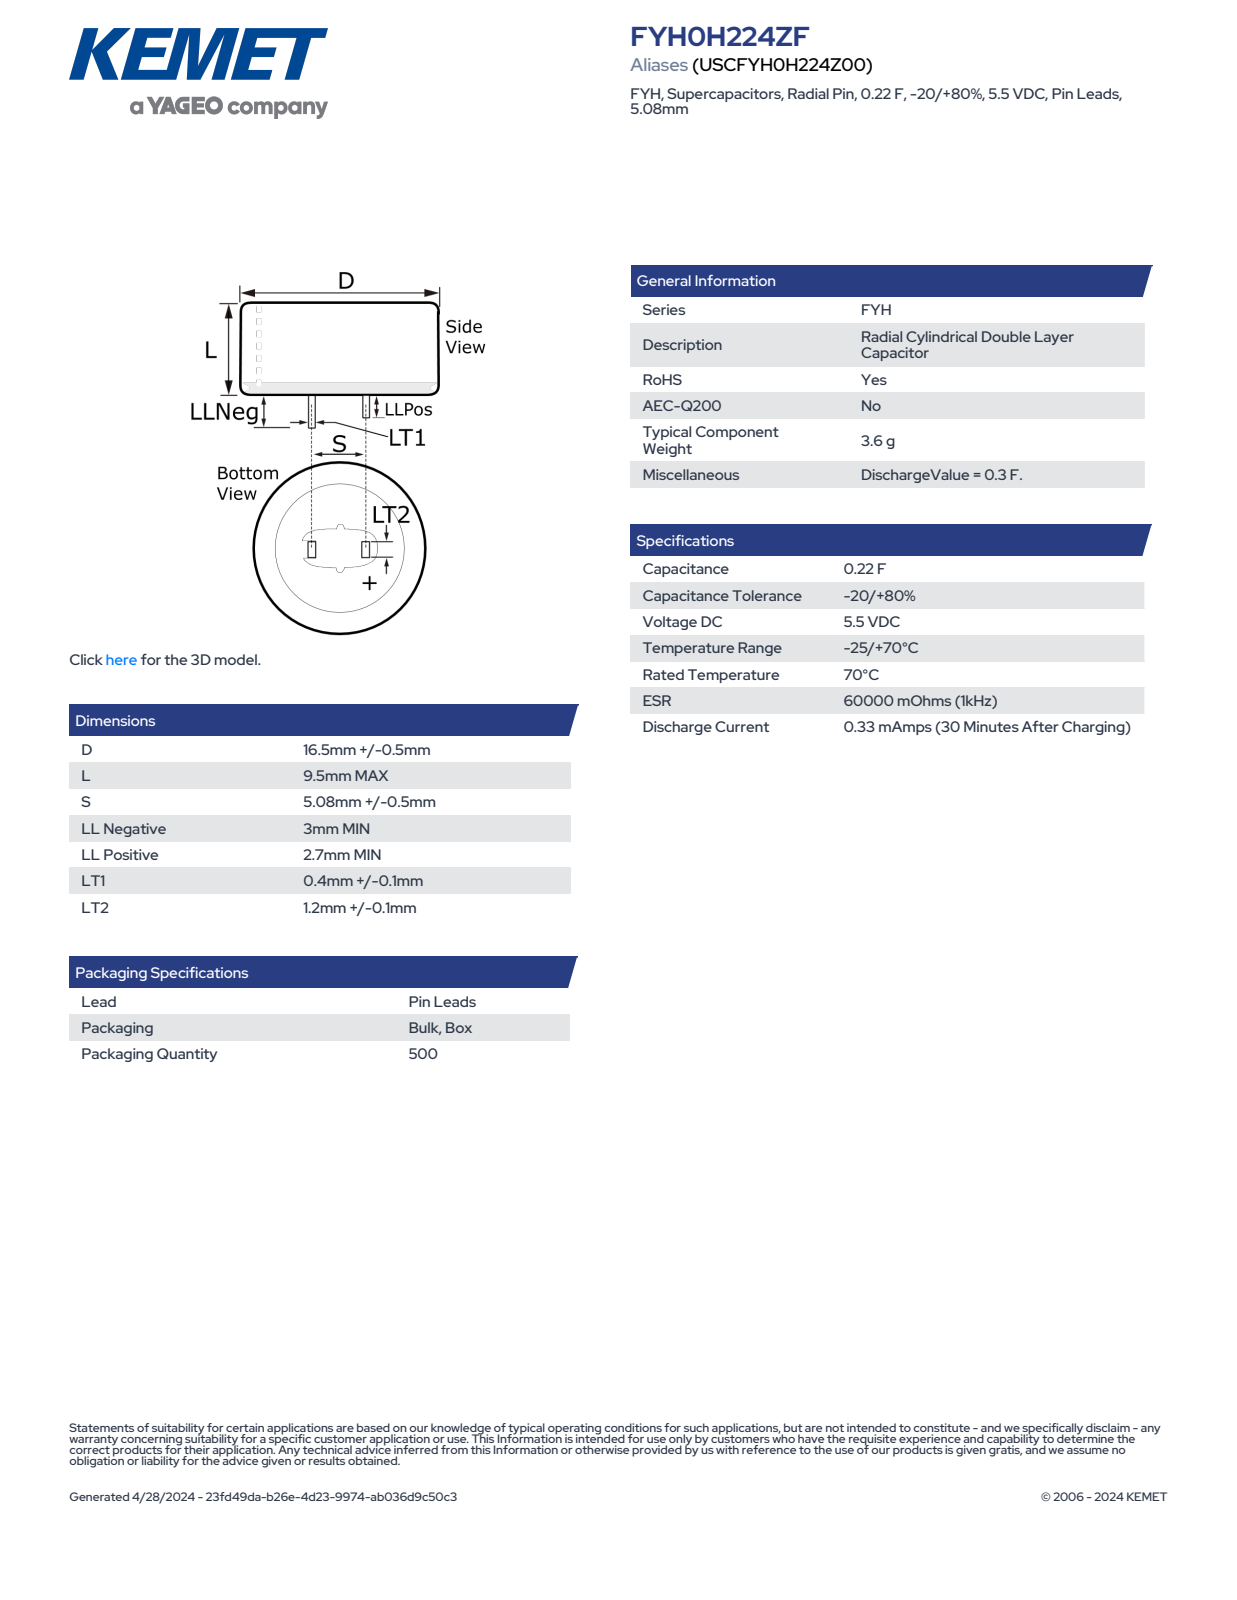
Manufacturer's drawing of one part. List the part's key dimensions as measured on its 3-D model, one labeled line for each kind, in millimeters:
Part name (STEP PRODUCT): CDR_LPLLN_D17L9.5S5.08LLNEG3LLPOS2.7LT10.5LT21.3
STEP written by: SolidWorks 2014 (AUTOMOTIVE_DESIGN)
Units: millimetres
Bodies: 1 solid, 78 faces (70 planar, 4 cylindrical, 4 other)
Overall size (bounding box): 17 × 17 × 12.5
Volume: 2 152 mm³ · Surface area: 954 mm²
Round bosses / shafts (diameter × count): ⌀17 ×1
Partial cylindrical surfaces — rounded edges, fillets, slot ends (radius × count): R8.51 ×1
Main face-to-face distances: 9.5, 9.49, 0.5, 5.08, 5.58, 4.58, 1.3, 3, 12.49, 12.5
